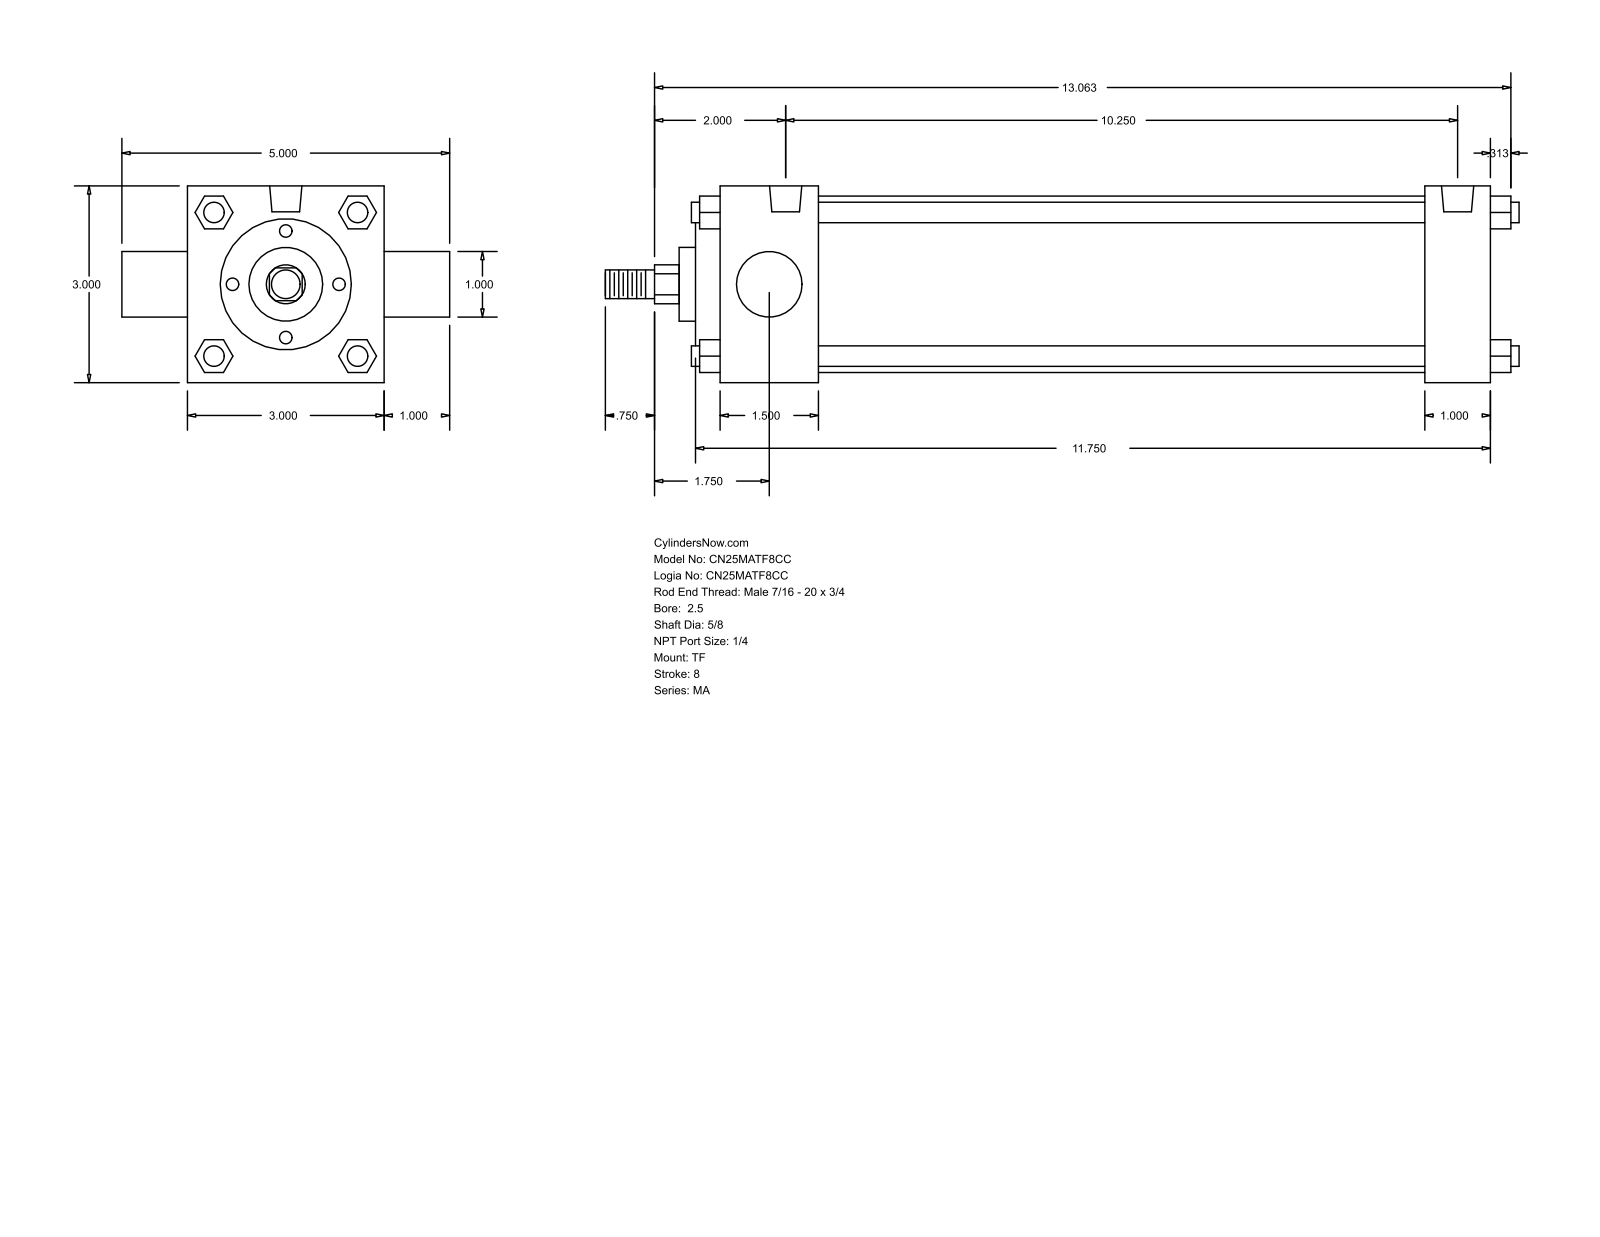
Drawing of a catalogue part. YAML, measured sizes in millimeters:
part_name: "MA_TF__0250_0.625"
step_written_by: "GSSL Pune (CONFIG_CONTROL_DESIGN)"
units: millimeters
bodies: {solids: 0, faces: 122, planar: 93, cylindrical: 29, other: 0}
overall_size: [354.01, 127, 76.2]
round_holes:
  - {diameter: 7.94, count: 3}
  - {diameter: 12.49, count: 2}
round_bosses_or_shafts:
  - {diameter: 7.94, count: 4}
  - {diameter: 68.33, count: 1}
  - {diameter: 50.8, count: 1}
  - {diameter: 28.57, count: 1}
  - {diameter: 25.4, count: 1}
  - {diameter: 15.88, count: 1}
  - {diameter: 11.11, count: 1}
partial_cylinders:
  - {radius: 7.54, count: 1}
face_to_face_distances: [76.2, 298.45, 25.4, 38.1, 273.05, 234.95, 260.35, 12.7, 9.52, 47.62]
hole_center_spacings: [260.35]
